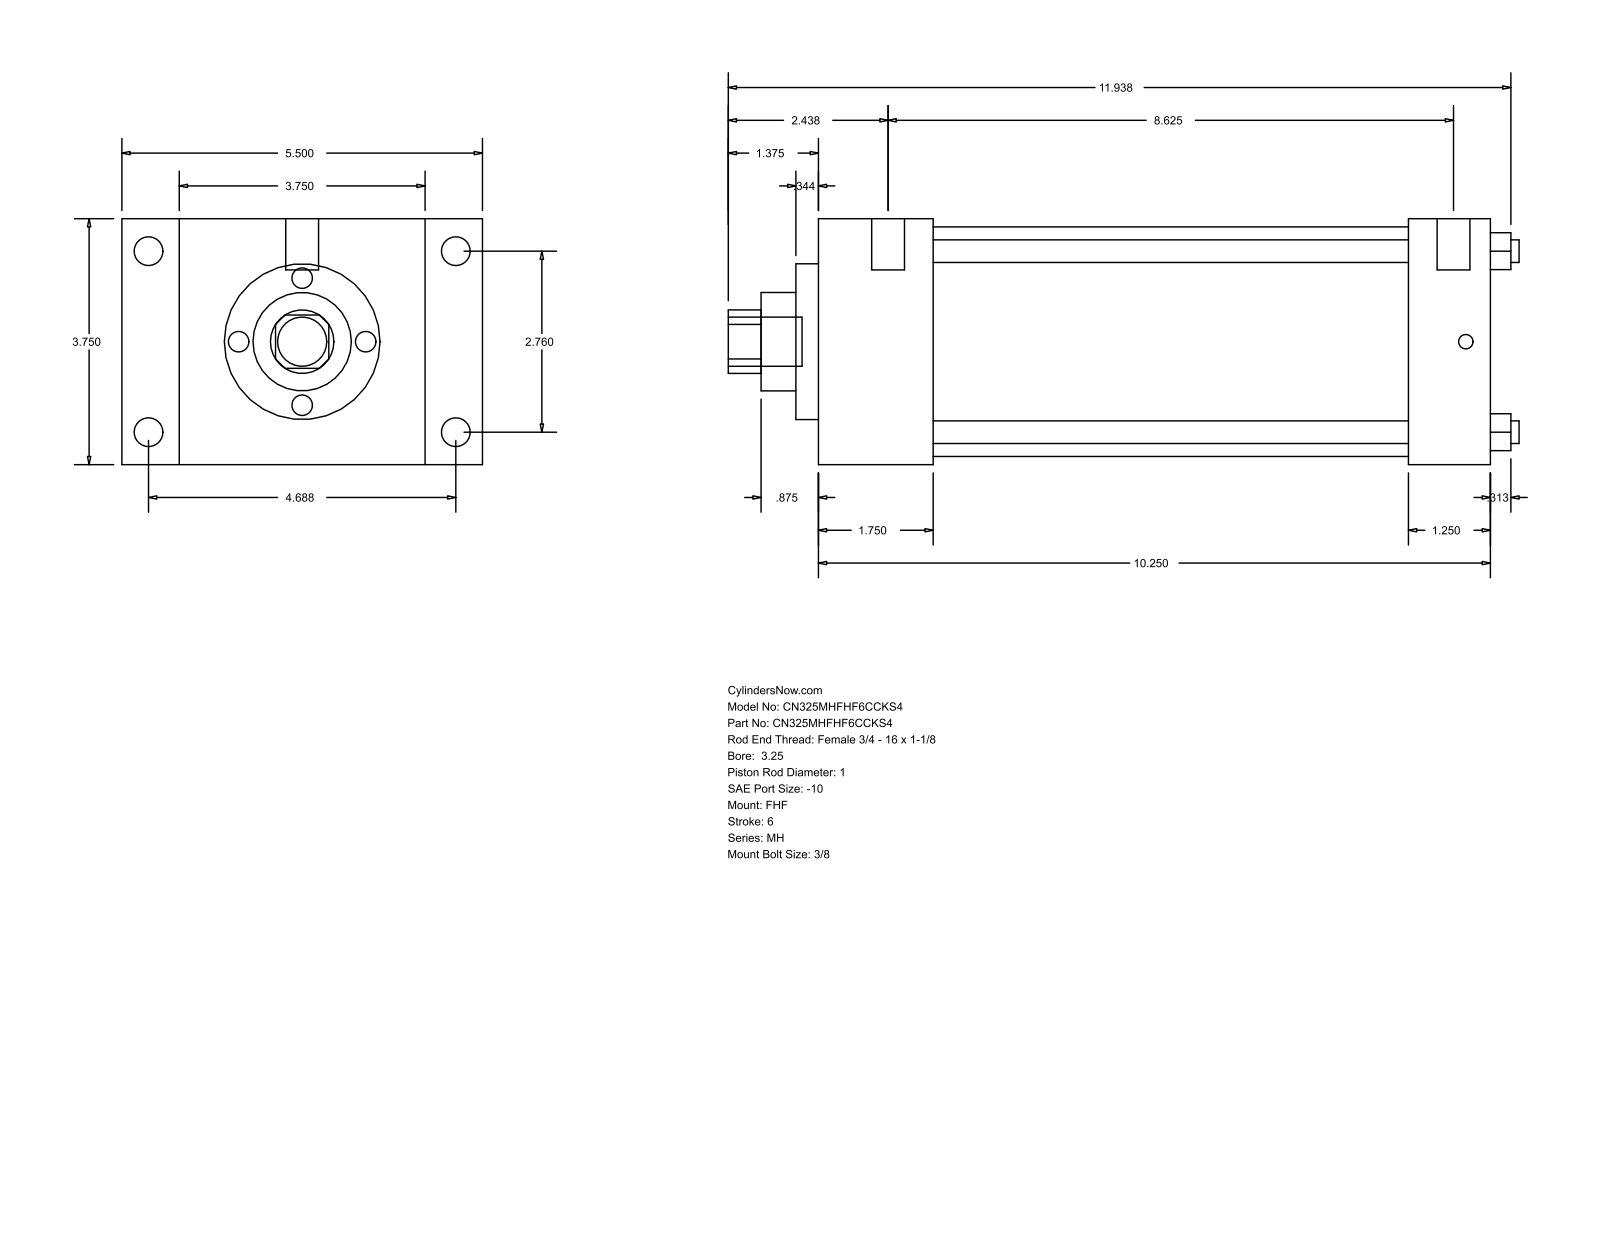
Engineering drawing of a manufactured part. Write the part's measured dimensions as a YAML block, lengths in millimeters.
part_name: "MH_FHF__0325_1"
step_written_by: "GSSL Pune (CONFIG_CONTROL_DESIGN)"
units: millimeters
bodies: {solids: 0, faces: 90, planar: 61, cylindrical: 29, other: 0}
overall_size: [306.39, 139.7, 95.25]
round_holes:
  - {diameter: 8.76, count: 4}
  - {diameter: 25.4, count: 1}
  - {diameter: 38.1, count: 1}
  - {diameter: 60.33, count: 1}
  - {diameter: 88.9, count: 1}
round_bosses_or_shafts:
  - {diameter: 11.13, count: 4}
  - {diameter: 5.56, count: 4}
  - {diameter: 12.7, count: 2}
  - {diameter: 19.05, count: 1}
partial_cylinders:
  - {radius: 12.29, count: 1}
face_to_face_distances: [95.24, 260.35, 44.46, 215.89, 22.23, 117.47, 139.7, 228.6, 184.14, 31.75]
hole_center_spacings: [49.57, 70.1, 99.14]
